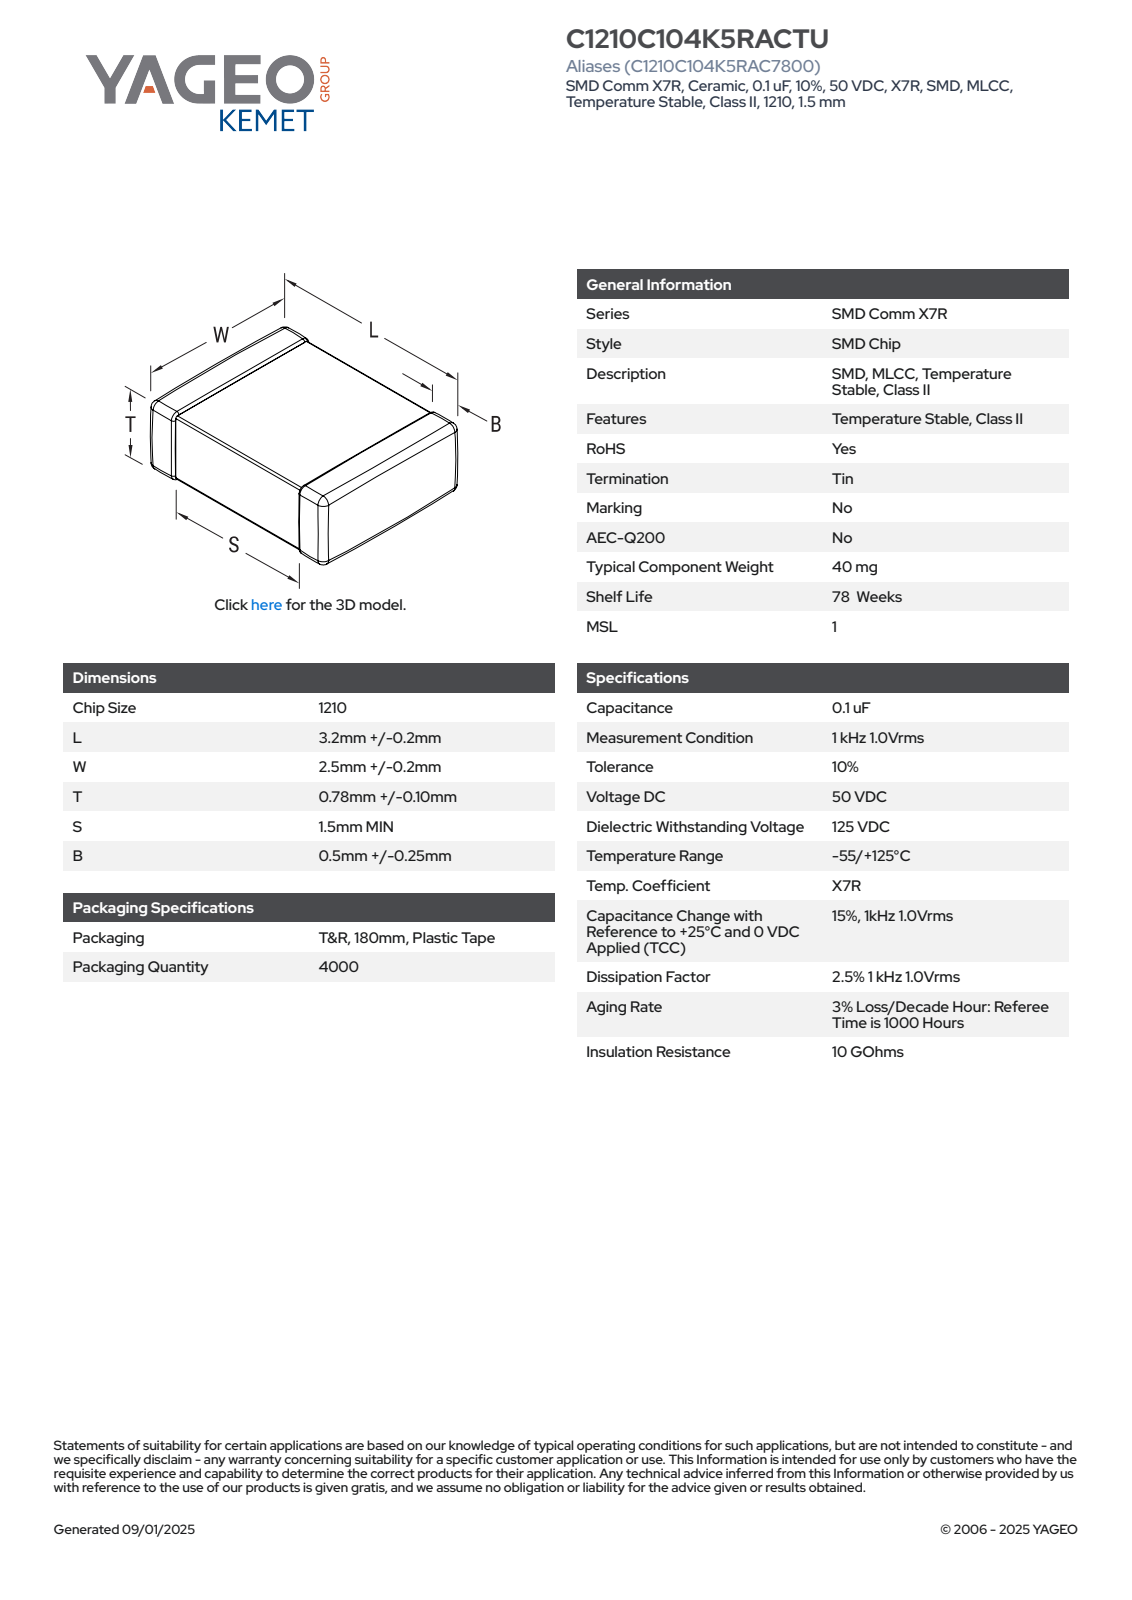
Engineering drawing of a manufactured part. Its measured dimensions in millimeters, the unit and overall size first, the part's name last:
Units: millimetres
Overall size (bounding box): 3.4 × 2.7 × 0.88
Main face-to-face distances: 0.82, 0.76, 0.88, 3.4, 2.64, 2.58, 2.7, 0.83, 0.77, 1.31
Volume: 7 mm³ · Surface area: 28 mm²
Bodies: 4 solids, 125 faces (71 planar, 38 cylindrical, 16 other)
Part name (STEP PRODUCT): CCS_CCSTDNOS_1210_L3.4W2.7T0.88B0.75
STEP written by: SolidWorks 2014 (AUTOMOTIVE_DESIGN)
